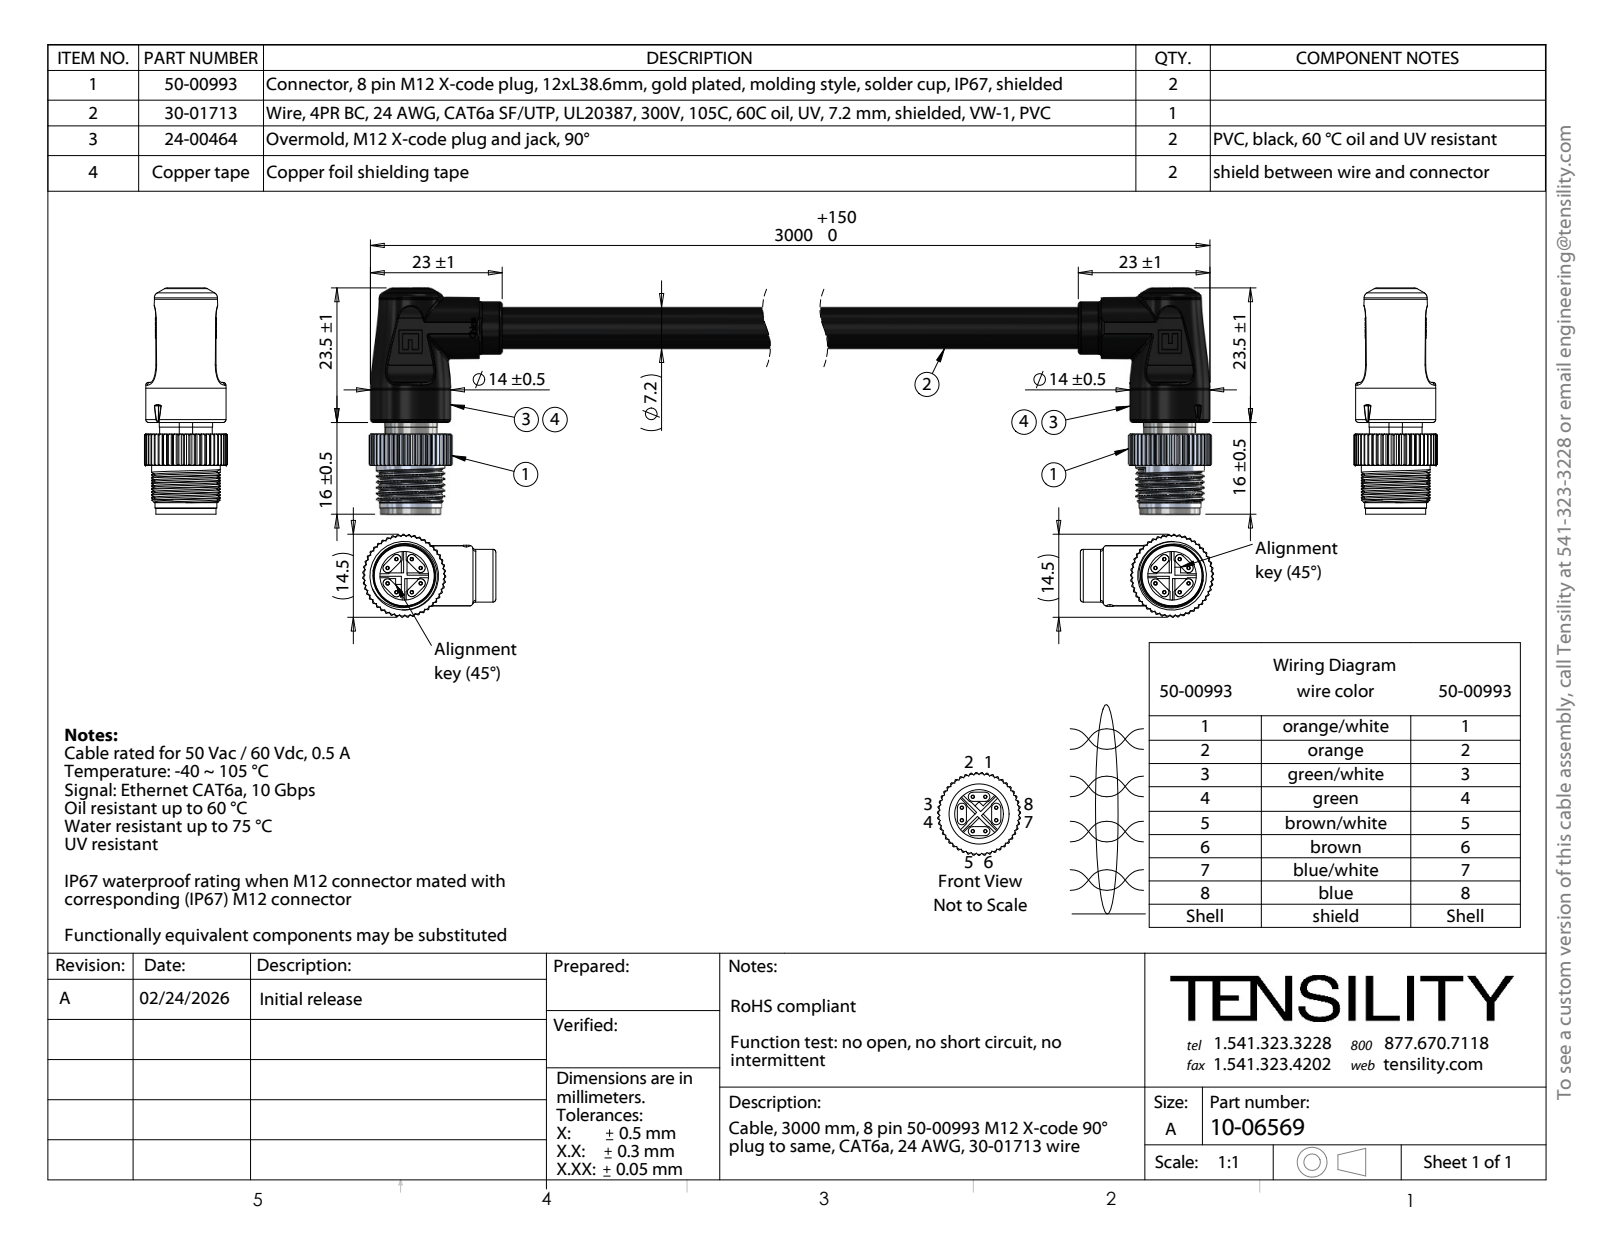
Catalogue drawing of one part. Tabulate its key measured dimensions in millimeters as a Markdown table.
| quantity | value |
| --- | --- |
| part name | 30-01713_blunt cut; 24-00464; 10-06569; 50-00993-05 (+5 more) |
| STEP written by | SolidWorks 2025 (CONFIG_CONTROL_DESIGN) |
| units | millimeters |
| bodies | 101 solids, 2561 faces (950 planar, 965 cylindrical, 646 other) |
| overall size | 196.49 × 39.5 × 14.5 |
| volume | 16 200 mm³ |
| surface area | 53 554 mm² |
| round holes (diameter × count) | 0.2 × 56, 0.6 × 16, 1.2 × 16, 2 × 2, 2.5 × 2, 7.5 × 2, 8.5 × 2, 9.07 × 2, 9.5 × 2, 5.03 × 1, 5.25 × 1, 5.65 × 1 |
| round bosses / shafts (diameter × count) | 1.4 × 16, 1.15 × 16, 0.8 × 16, 1.05 × 8, 9.2 × 3, 14 × 2, 12 × 2, 11 × 2 |
| partial cylindrical surfaces (radius × count) | 0.8 × 16, 1 × 16, 0.1 × 12, 0.5 × 8, 2.17 × 8, 7.25 × 2 |
| main face-to-face distances | 0.5, 2, 6, 128.67, 5.5, 0.99, 0.98, 5, 16.25, 16.75 |
| hole center spacings | 3.19, 0.35, 4.51, 1.61, 1.78, 0.41, 182, 1.06 |
